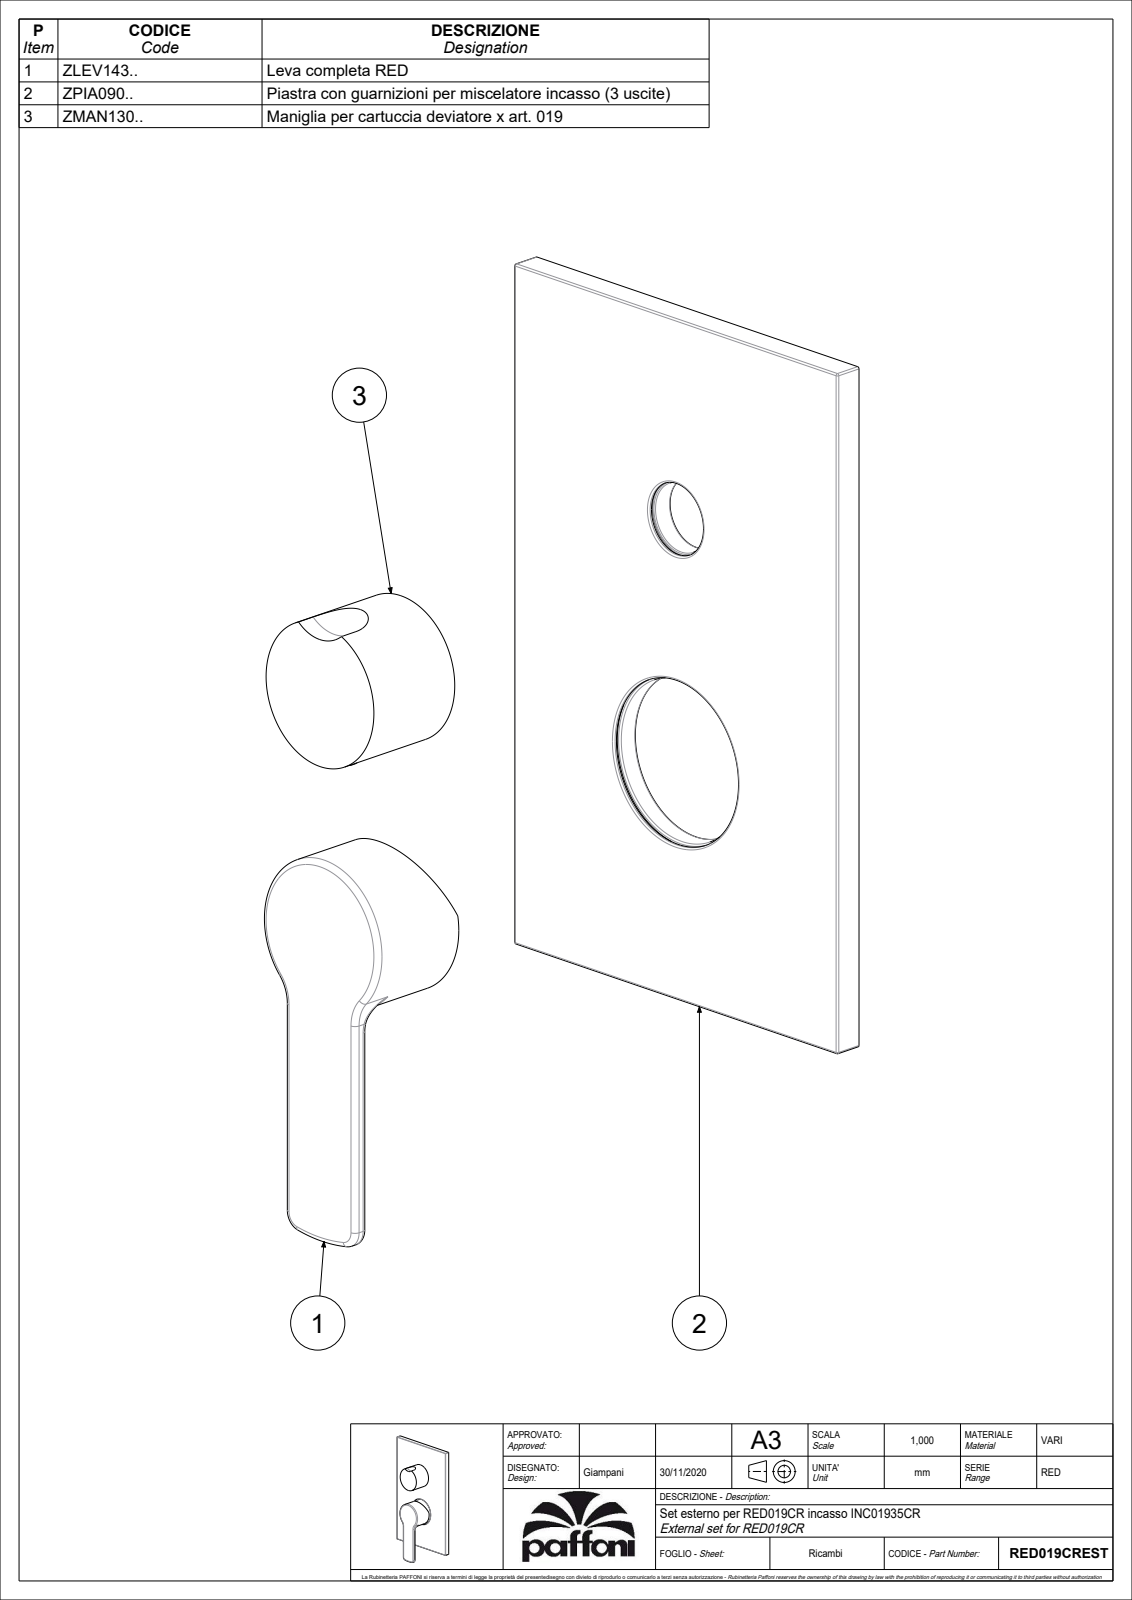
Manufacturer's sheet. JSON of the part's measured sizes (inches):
{"part_name": "RED018CREST", "step_written_by": "CREO PARAMETRIC BY PTC INC, 2020044 (CONFIG_CONTROL_DESIGN)", "units": "inches", "bodies": {"solids": 3, "faces": 396, "planar": 116, "cylindrical": 144, "other": 136}, "overall_size": [8.228, 4.724, 1.589], "volume_in3": 9.782, "surface_area_in2": 156.5, "round_holes": [[0.118, 2], [0.126, 1], [0.13, 1], [0.165, 1], [0.177, 1], [0.583, 1], [0.756, 1], [0.787, 1], [0.827, 1], [0.913, 1], [1.417, 1], [1.772, 1]], "round_bosses_or_shafts": [[0.299, 2], [0.217, 2], [2.008, 1], [1.929, 1], [1.693, 1], [1.575, 1], [0.984, 1], [0.945, 1]], "partial_cylinders_radius": [[0.02, 47], [0.039, 8], [0.059, 4], [0.197, 2], [0.394, 2], [0.492, 1], [1.969, 1]], "face_to_face_distances": [0.098, 0.315, 0.217, 0.02, 0.197, 0.118, 1.181, 0.886, 1.083, 1.398], "hole_center_spacings": [0.236, 0.394, 2.677, 3.071]}
